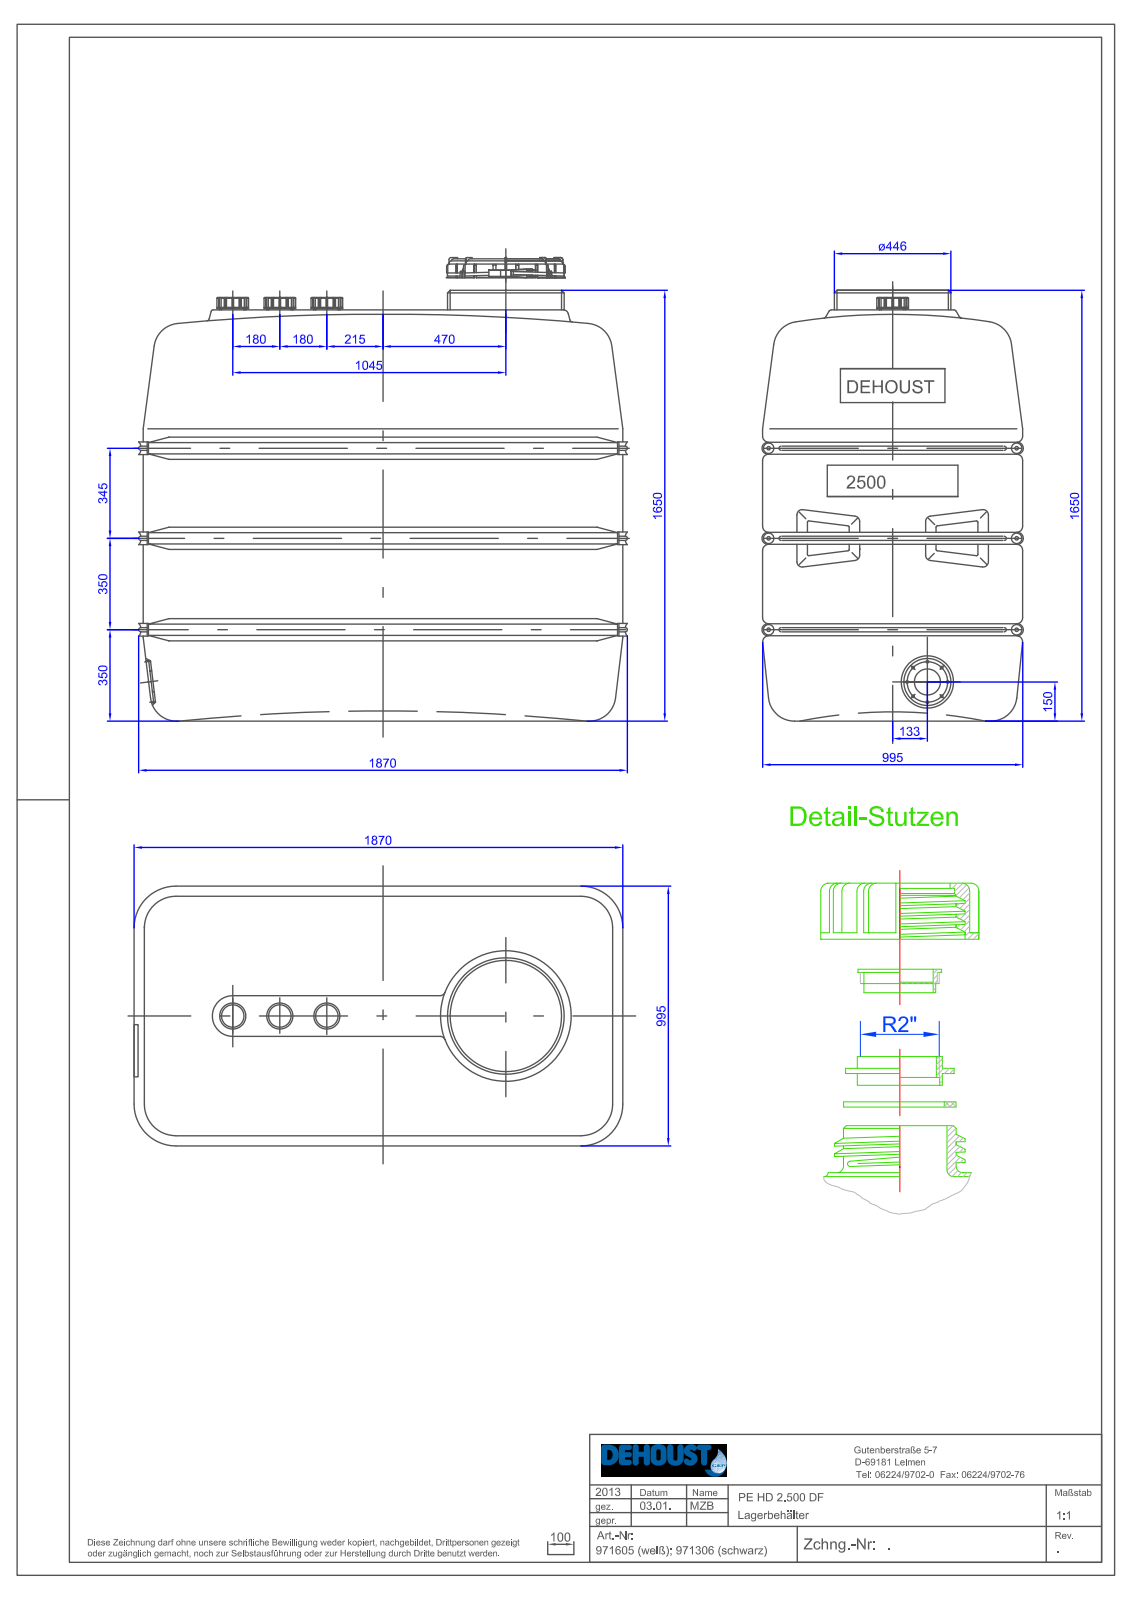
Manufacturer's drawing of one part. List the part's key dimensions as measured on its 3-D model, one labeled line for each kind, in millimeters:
Part name (STEP PRODUCT): PE-DF2500; Skizze2500; Boden; Deckelaufbau1 (+8 more)
STEP written by: Autodesk Inventor 2011 (AUTOMOTIVE_DESIGN)
Units: millimetres
Bodies: 85 solids, 1490 faces (715 planar, 429 cylindrical, 346 other)
Overall size (bounding box): 1887.26 × 1654.47 × 995.04
Volume: 52 090 000 mm³ · Surface area: 32 160 000 mm²
Round holes (diameter × count): ⌀10 ×12, ⌀10.11 ×12, ⌀13 ×12, ⌀7 ×8, ⌀48 ×7, ⌀82.31 ×3, ⌀85 ×3, ⌀69.85 ×1, ⌀362.02 ×1, ⌀365.76 ×1, ⌀395.51 ×1, ⌀429 ×1
Round bosses / shafts (diameter × count): ⌀39.1 ×12, ⌀24 ×12, ⌀17.2 ×12, ⌀12 ×12, ⌀11.05 ×12, ⌀8 ×8, ⌀50 ×6, ⌀105 ×3
Partial cylindrical surfaces — rounded edges, fillets, slot ends (radius × count): R27 ×30, R30 ×30, R97 ×17, R100 ×17, R2 ×16, R7 ×14, R14.46 ×12, R16.75 ×12
Main face-to-face distances: 3, 2.98, 1547.02, 992, 3.02, 991.97, 2.97, 1867.03, 1550, 1550.02
Hole centre spacings: 920.59, 67.59, 51.73, 124.87, 67.57, 67.58, 95.57, 95.58
